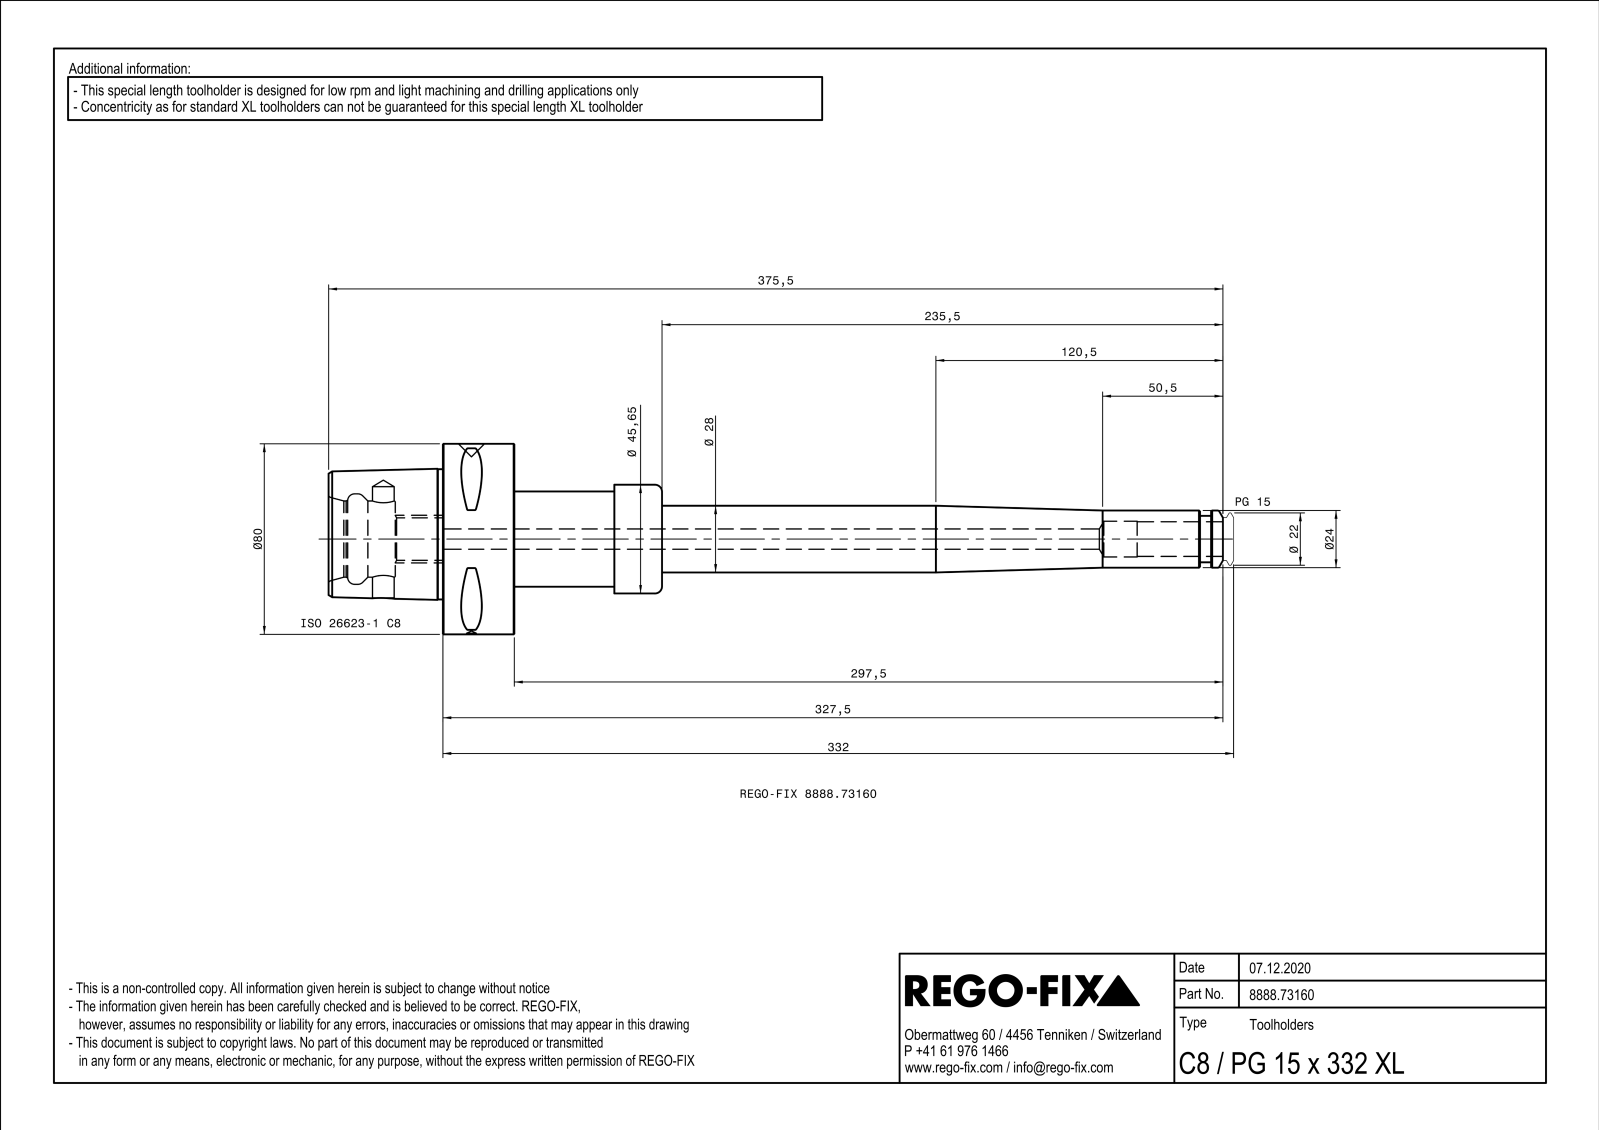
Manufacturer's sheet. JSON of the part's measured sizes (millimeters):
{"part_name": "NOCUT", "step_written_by": "SIEMENS PLM Software Solid Edge ST10 (AUTOMOTIVE_DESIGN)", "units": "millimeters", "bodies": {"solids": 1, "faces": 165, "planar": 36, "cylindrical": 37, "other": 92}, "overall_size": [375.5, 80, 80], "volume_mm3": 391223, "surface_area_mm2": 77999, "round_holes": [[4, 1], [9, 1], [9.1, 1], [10, 1], [13, 1], [15, 1], [17.84, 1], [25, 1], [29, 1], [32, 1], [38, 1], [38.38, 1]], "round_bosses_or_shafts": [[80, 1], [45.65, 1], [40, 1], [34, 1], [33, 1], [28, 1], [24.7, 1], [24, 1]], "partial_cylinders_radius": [[0.5, 8], [22.77, 1]], "face_to_face_distances": [30, 48, 78, 92, 20, 62, 140, 32.55, 50, 112], "hole_center_spacings": [37]}
